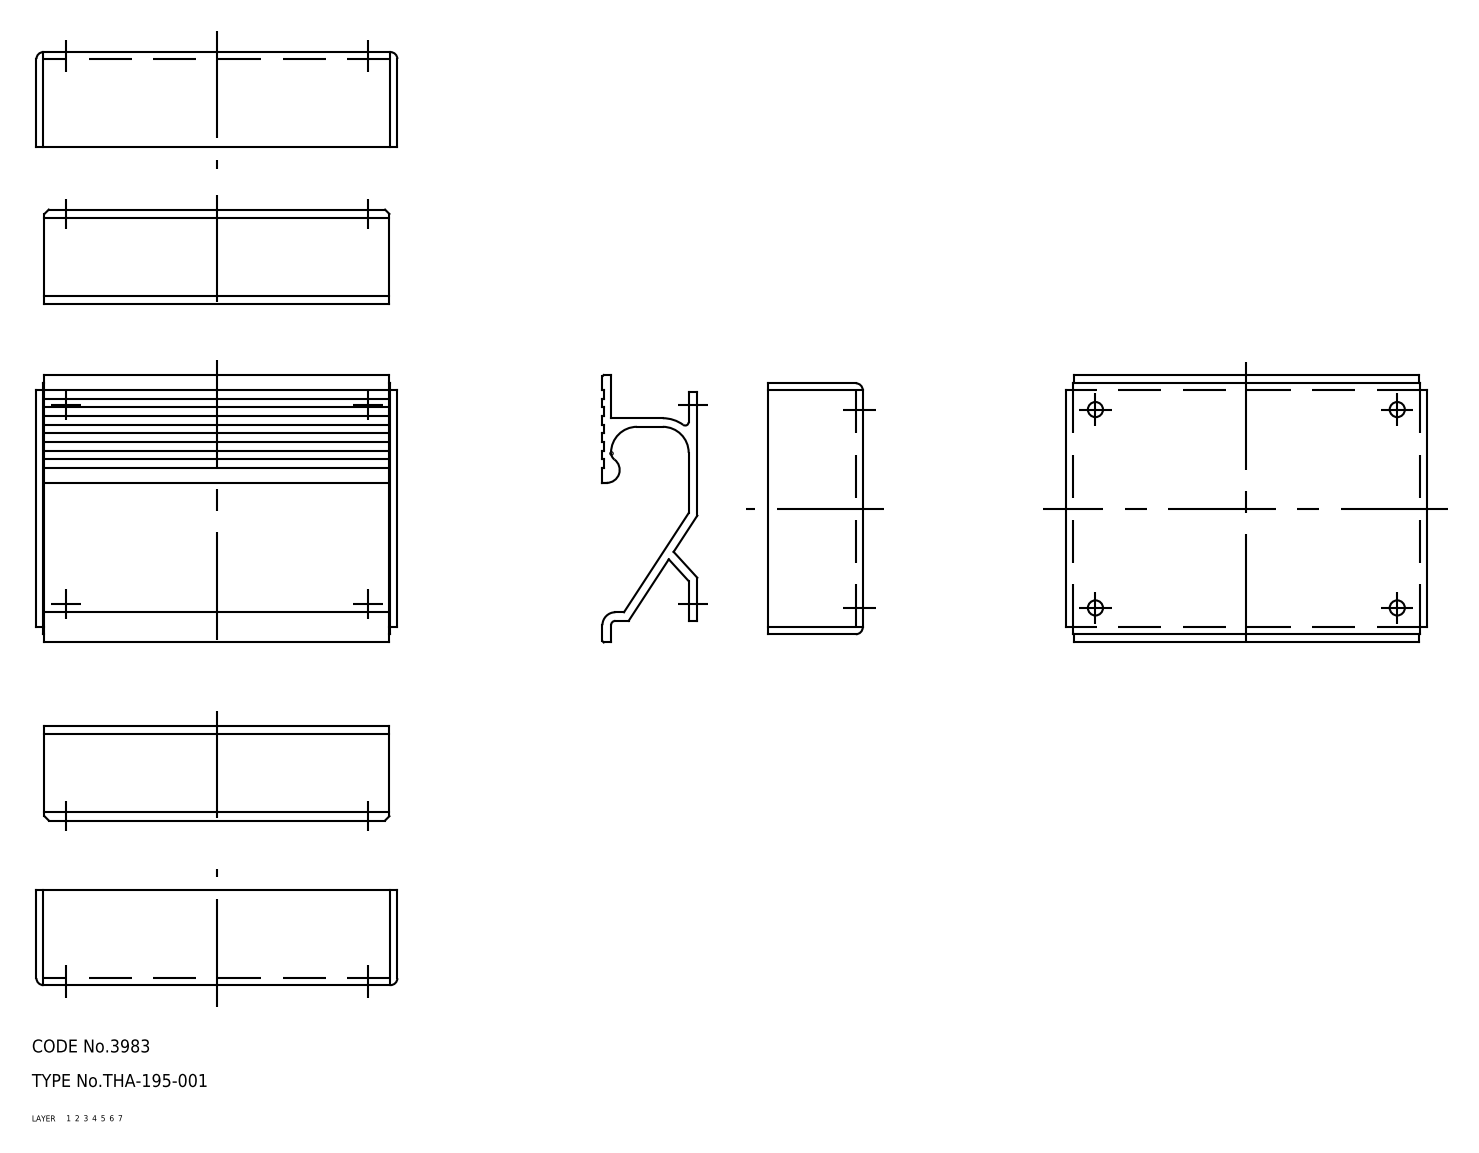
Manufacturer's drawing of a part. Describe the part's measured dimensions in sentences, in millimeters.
The part is named "pull; bracket; THA_195_001_2780_36". Its 3-D file was written by "CADfix (AUTOMOTIVE_DESIGN)". It is 2 solids with 101 faces: 0 planar, 0 cylindrical and 101 other. Overall it measures 83.7 by 62 by 24 millimeters. Its volume is 37 816 cubic millimeters and its surface area 42 384 square millimeters.
